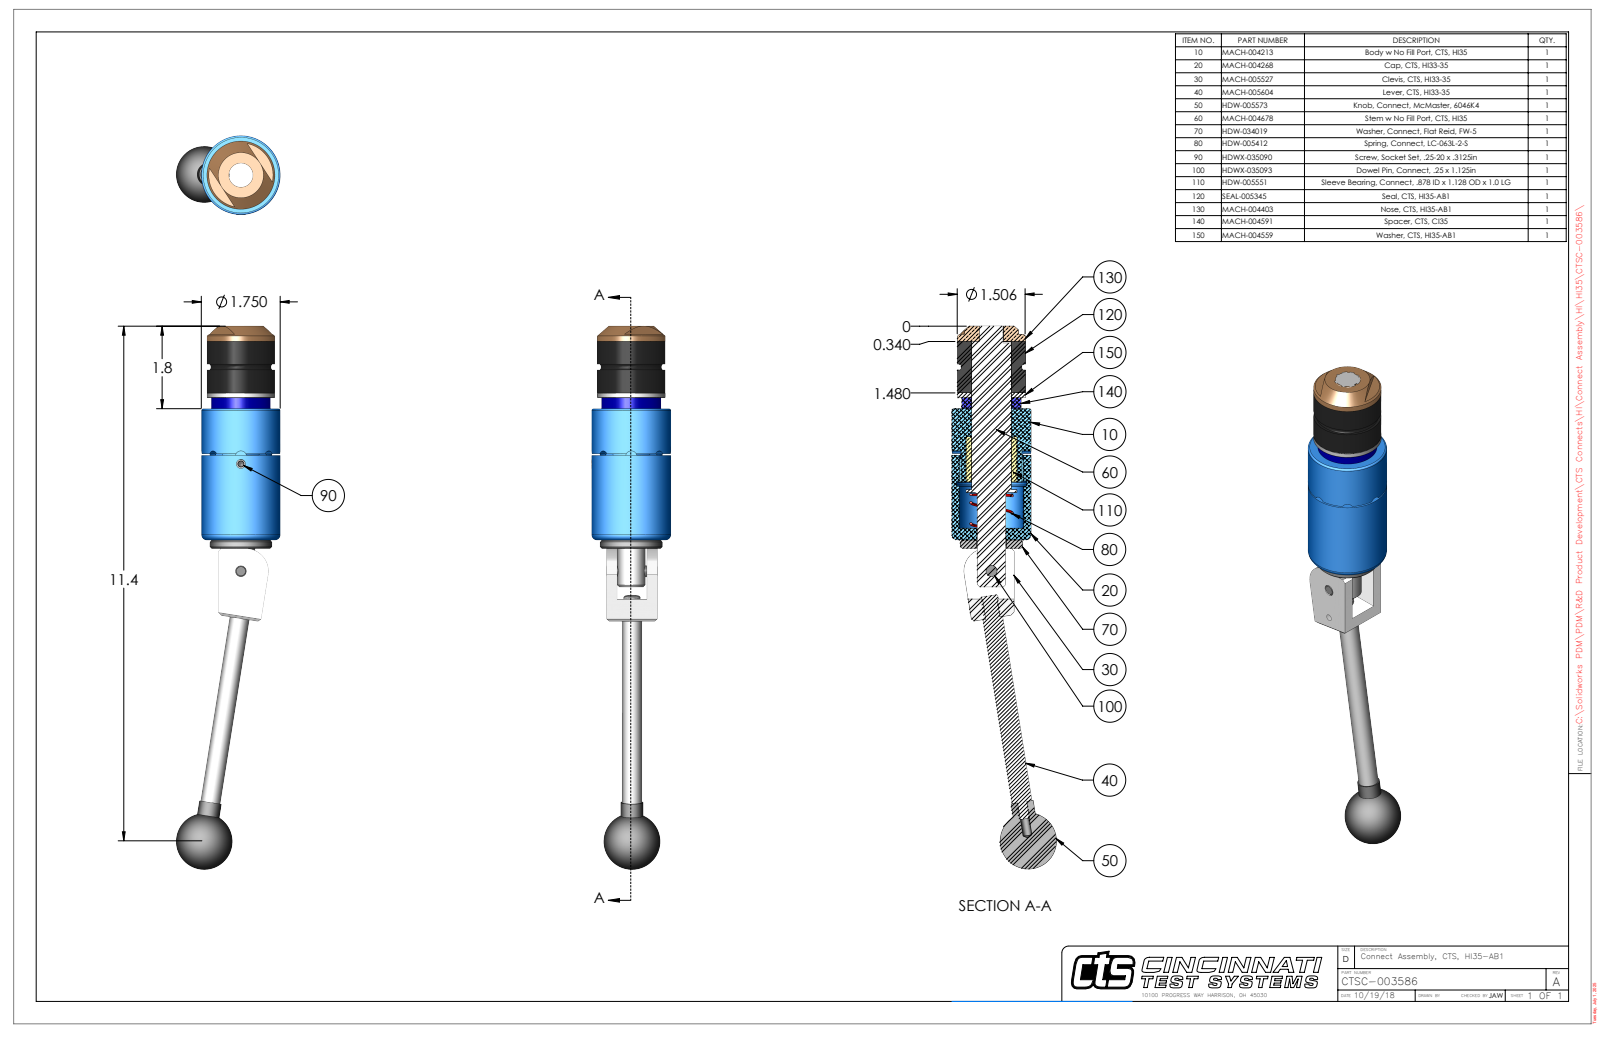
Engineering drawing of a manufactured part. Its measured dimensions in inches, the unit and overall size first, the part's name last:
Units: inches
Overall size (bounding box): 12.039 × 2.312 × 1.75
Round holes (diameter × count): ⌀0.201 ×2, ⌀0.15 ×1, ⌀0.249 ×1, ⌀0.251 ×1, ⌀0.313 ×1, ⌀0.531 ×1, ⌀0.635 ×1, ⌀0.656 ×1, ⌀0.875 ×1, ⌀0.876 ×1, ⌀0.885 ×1, ⌀1.419 ×1
Round bosses / shafts (diameter × count): ⌀0.25 ×2, ⌀1.75 ×1, ⌀1.506 ×1, ⌀1.38 ×1, ⌀1.312 ×1, ⌀0.871 ×1, ⌀0.869 ×1, ⌀0.625 ×1
Partial cylindrical surfaces — rounded edges, fillets, slot ends (radius × count): R0.125 ×5, R0.029 ×2, R0.5 ×1, R0.695 ×1, R0.82 ×1
Main face-to-face distances: 4.402, 1.49, 2.912, 1.14, 0.35, 3.262, 0.11, 1.25, 0.24, 3.152
Hole centre spacings: 0.74, 2.376, 3.116
Volume: 13.15 in³ · Surface area: 80.48 in²
Bodies: 10 solids, 262 faces (94 planar, 105 cylindrical, 63 other)
Part name (STEP PRODUCT): CTSC-003586
STEP written by: SolidWorks 2023 (AUTOMOTIVE_DESIGN)
